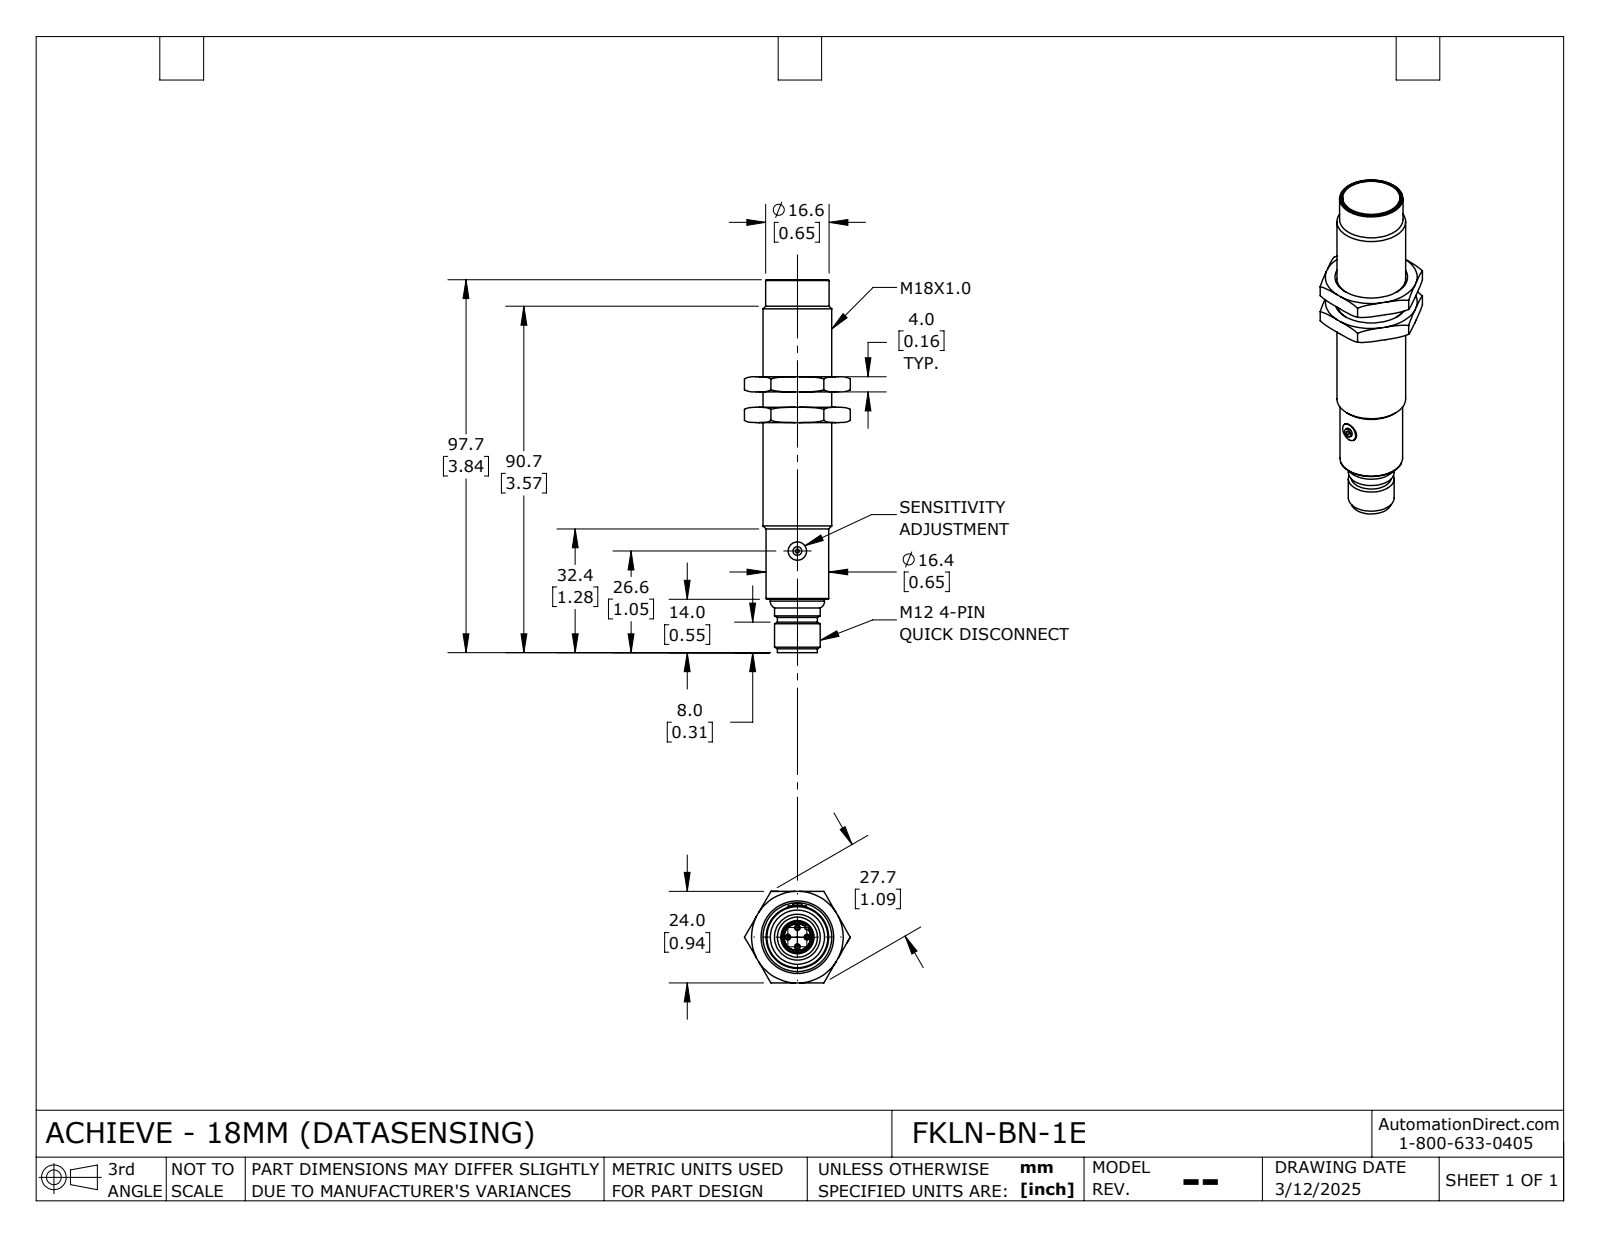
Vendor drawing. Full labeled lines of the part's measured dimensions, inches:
Part name (STEP PRODUCT): FKLN-BN-1E_Default
STEP written by: SolidWorks 2024 (CONFIG_CONTROL_DESIGN)
Units: inches
Bodies: 3 solids, 121 faces (43 planar, 29 cylindrical, 49 other)
Overall size (bounding box): 3.844 × 1.091 × 0.945
Volume: 1.404 in³ · Surface area: 14.06 in²
Round holes (diameter × count): ⌀0.185 ×1, ⌀0.278 ×1, ⌀0.327 ×1, ⌀0.587 ×1, ⌀0.709 ×1
Round bosses / shafts (diameter × count): ⌀0.039 ×4, ⌀0.654 ×1, ⌀0.646 ×1, ⌀0.591 ×1, ⌀0.583 ×1, ⌀0.559 ×1, ⌀0.472 ×1, ⌀0.413 ×1
Partial cylindrical surfaces — rounded edges, fillets, slot ends (radius × count): R0.02 ×2, R0.024 ×1, R0.297 ×1
Main face-to-face distances: 0.157, 0.315, 0.945, 0.093, 0.1, 1.215, 1.222, 1.315, 0.9, 0.907
